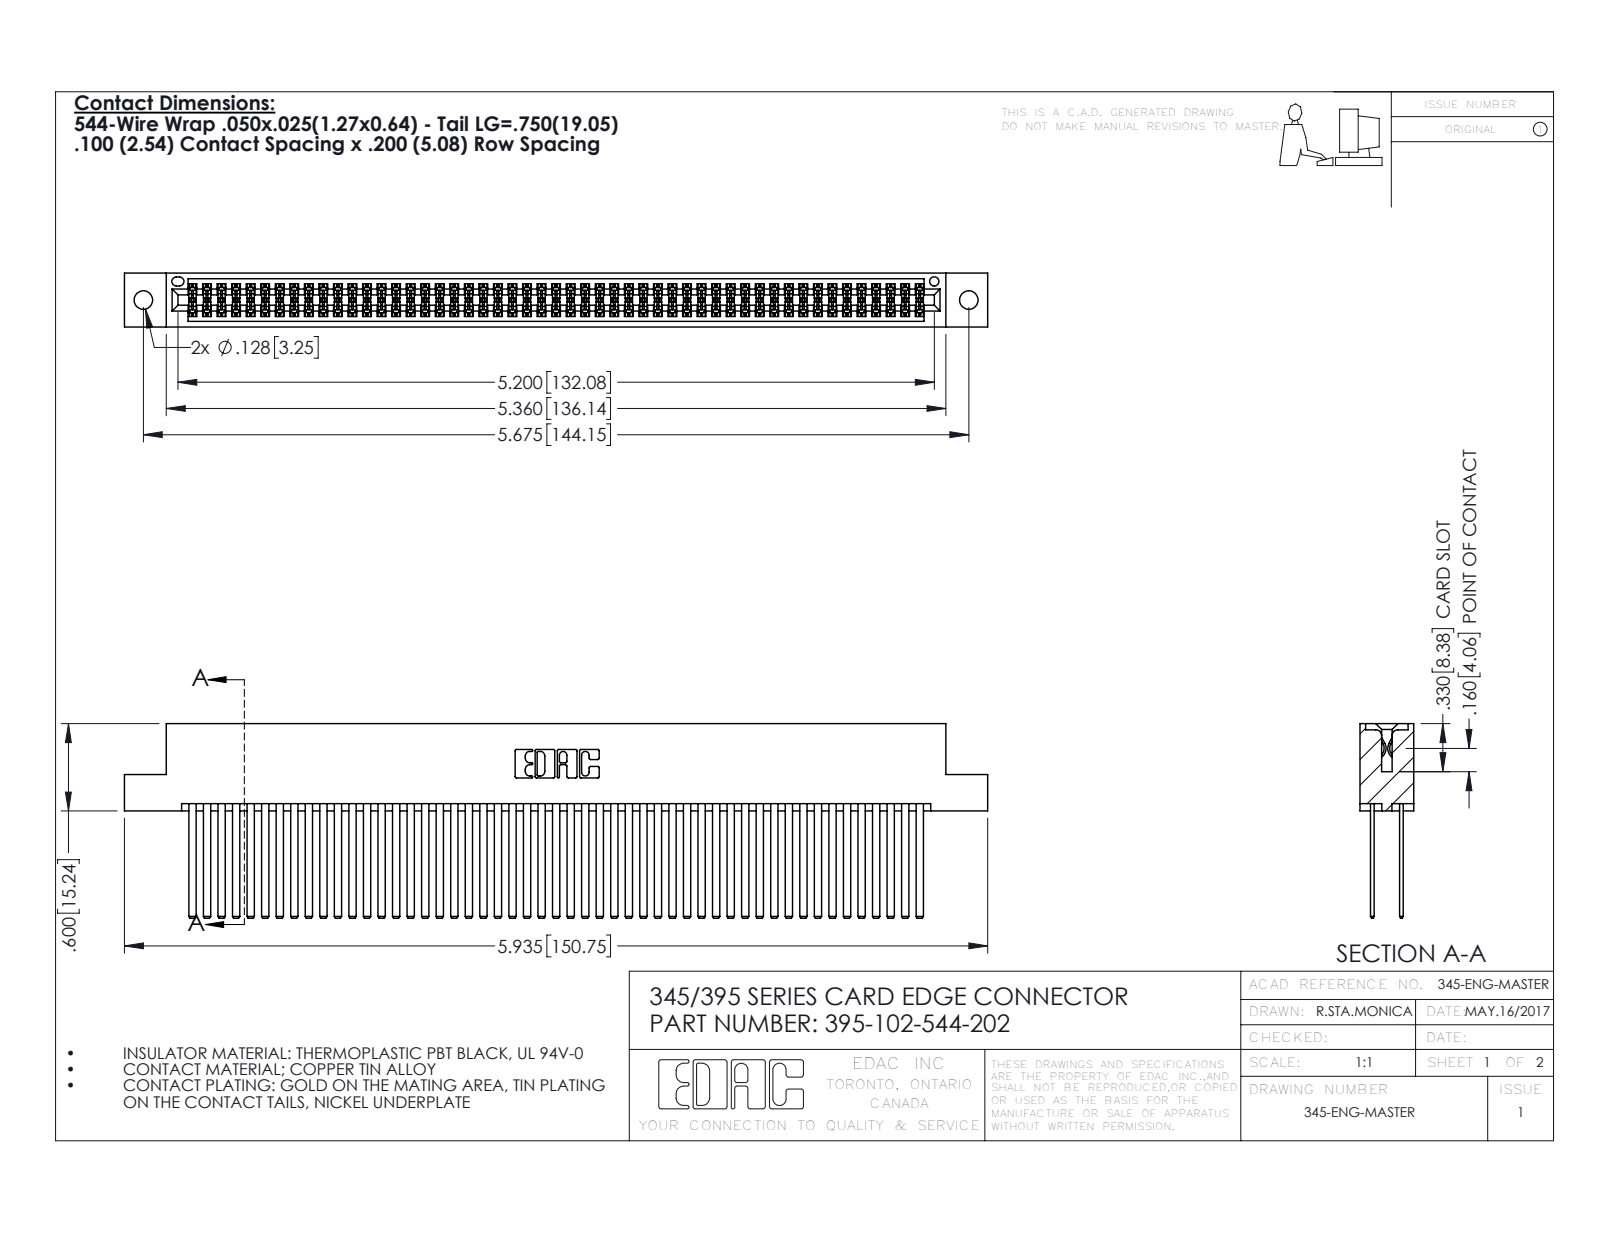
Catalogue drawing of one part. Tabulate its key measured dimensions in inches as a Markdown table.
| quantity | value |
| --- | --- |
| part name | 345-292-001_345-293-144; 345 Part_Flush Mounting Lugs - 0.128 Dia; 395-102-544-202 |
| STEP written by | SolidWorks 2016 (CONFIG_CONTROL_DESIGN) |
| units | inches |
| bodies | 103 solids, 4614 faces (3038 planar, 1576 cylindrical, 0 other) |
| overall size | 5.935 × 1.337 × 0.37 |
| volume | 0.984 in³ |
| surface area | 43.28 in² |
| round holes (diameter × count) | 0.128 × 2, 0.064 × 1 |
| partial cylindrical surfaces (radius × count) | 0.006 × 153, 0.01 × 22, 0.007 × 6, 0.031 × 6, 0.026 × 3, 0.014 × 2, 0.019 × 2, 0.022 × 2 |
| main face-to-face distances | 0.2, 0.025, 0.298, 0.072, 0.098, 0.272, 0.225, 0.175, 0.37, 0.05 |
| hole center spacings | 0.27, 5.439, 5.675 |
